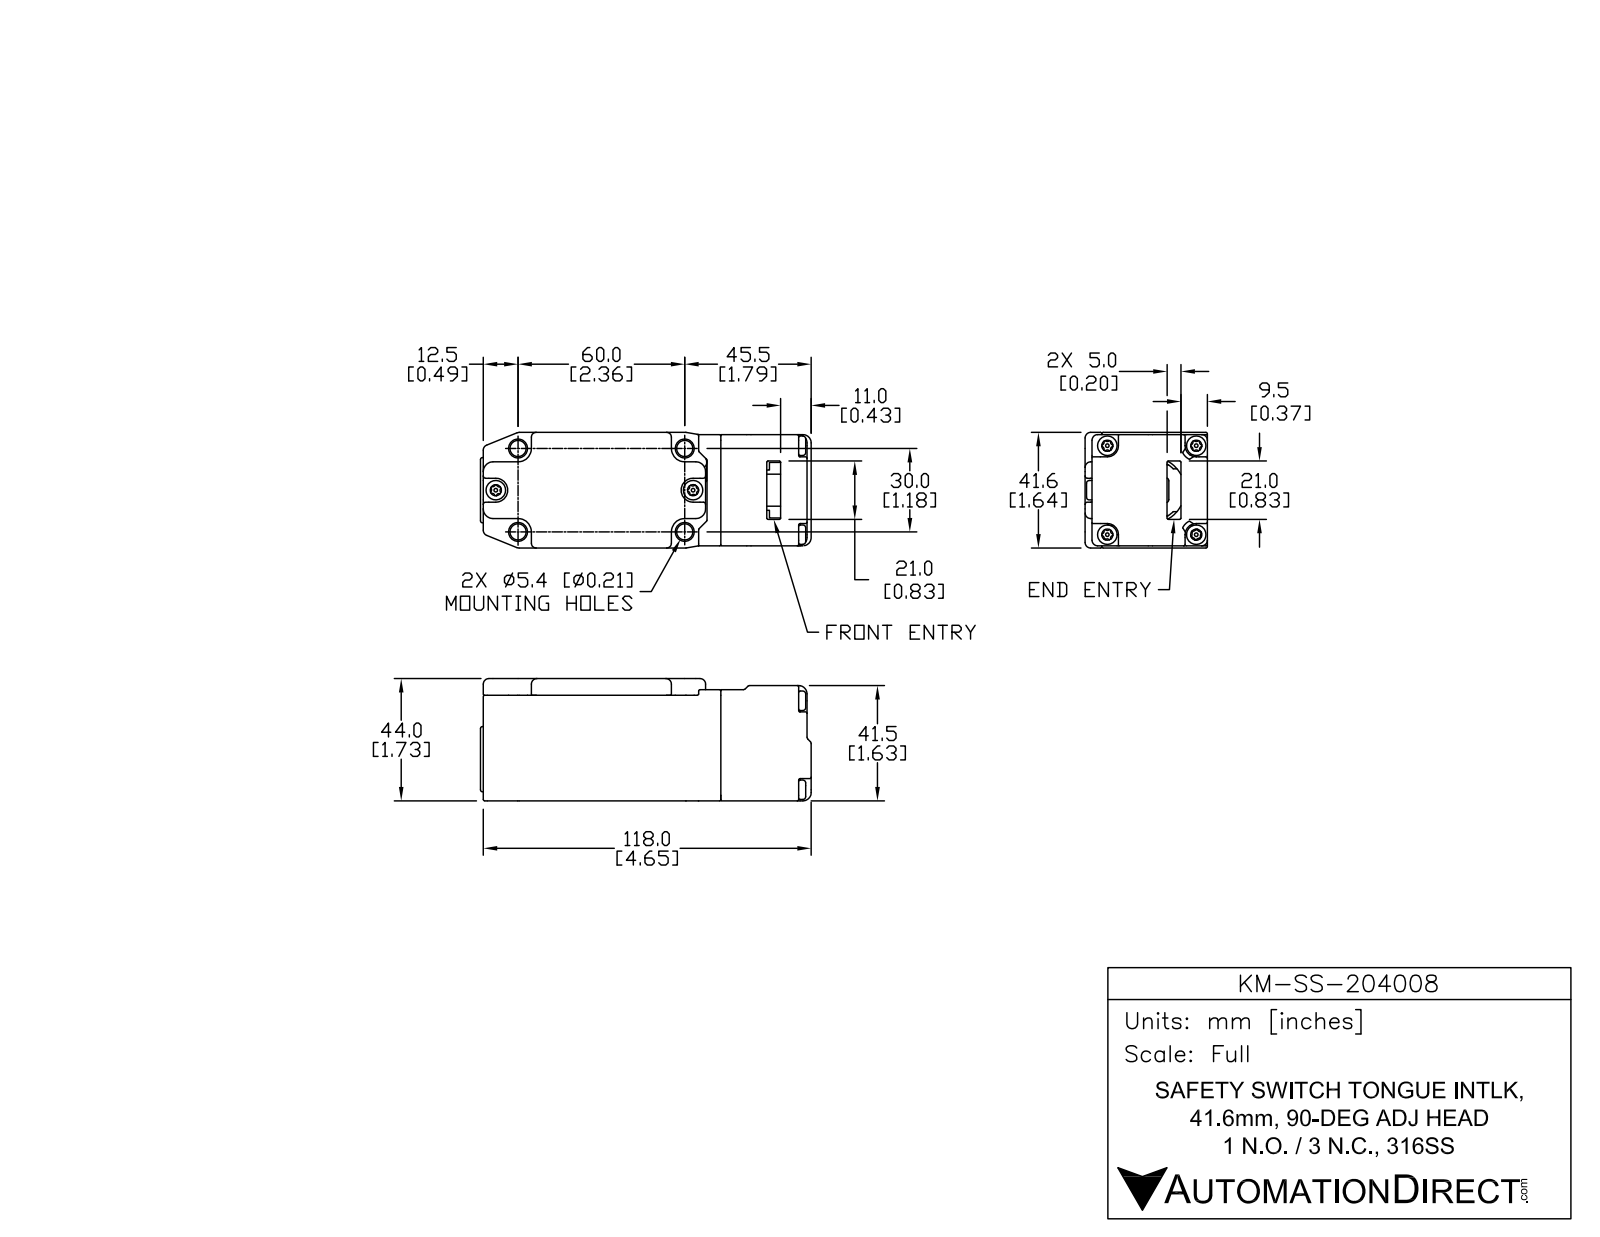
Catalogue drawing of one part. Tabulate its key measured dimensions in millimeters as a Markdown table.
| quantity | value |
| --- | --- |
| part name | KM-SS-204008 |
| STEP written by | SolidWorks 2013 (AUTOMOTIVE_DESIGN) |
| units | millimeters |
| bodies | 1 solid, 632 faces (120 planar, 278 cylindrical, 234 other) |
| overall size | 119.63 × 44.06 × 41.6 |
| volume | 190 045 mm³ |
| surface area | 28 649 mm² |
| round holes (diameter × count) | 5.4 × 4 |
| round bosses / shafts (diameter × count) | 5.5 × 4, 6.63 × 2, 23 × 1, 5.6 × 1 |
| partial cylindrical surfaces (radius × count) | 0.25 × 134, 0.5 × 43, 5 × 6, 3 × 5, 1 × 4, 1.7 × 4, 2.25 × 2, 2.5 × 2 |
| main face-to-face distances | 41.6, 0.8, 40.8, 44, 40, 0.5, 43.5, 5, 118, 2.6 |
| hole center spacings | 32, 60, 68 |
